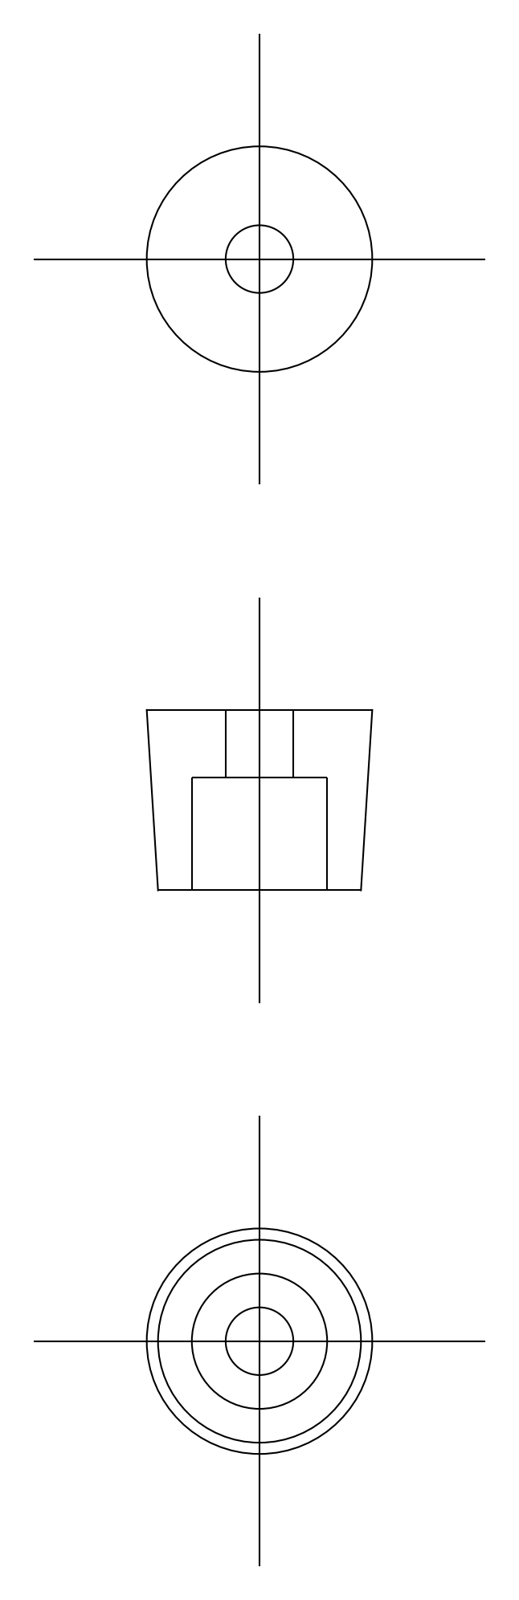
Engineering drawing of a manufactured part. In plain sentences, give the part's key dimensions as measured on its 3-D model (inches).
The part is named "washer; rubber foot; UK_7_10912_36". Its 3-D file was written by "CADfix (AUTOMOTIVE_DESIGN)". It is 2 solids with 21 faces: 0 planar, 0 cylindrical and 21 other. Overall it measures 0.394 by 0.394 by 0.315 inches. Its volume is 0.025 cubic inches and its surface area 1 square inches.
